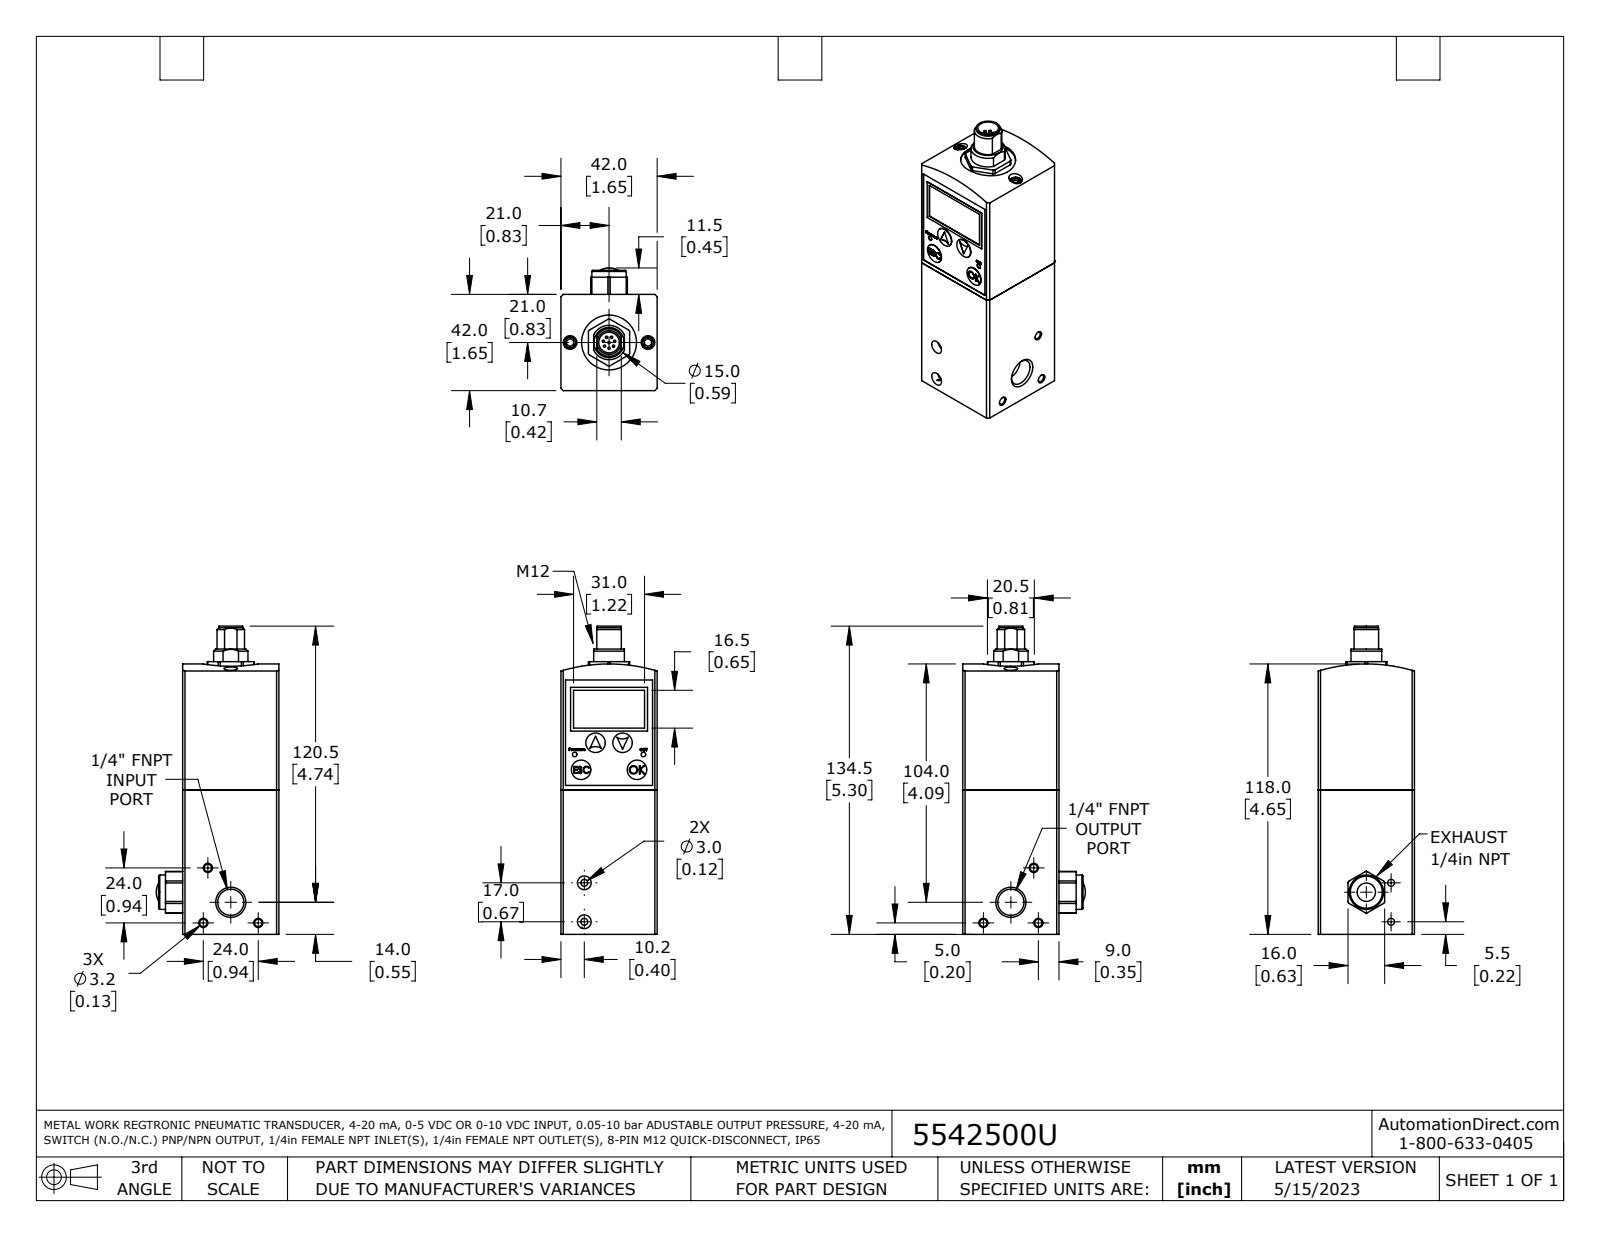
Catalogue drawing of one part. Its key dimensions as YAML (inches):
part_name: "5542500U"
step_written_by: "SolidWorks 2021 (AUTOMOTIVE_DESIGN)"
units: inches
bodies: {solids: 1, faces: 538, planar: 243, cylindrical: 248, other: 47}
overall_size: [5.295, 2.107, 1.654]
volume: 12.62
surface_area: 42.23
round_holes:
  - {diameter: 0.236, count: 8}
  - {diameter: 0.128, count: 3}
  - {diameter: 0.03, count: 2}
  - {diameter: 0.079, count: 2}
  - {diameter: 0.118, count: 2}
  - {diameter: 0.041, count: 1}
  - {diameter: 0.145, count: 1}
  - {diameter: 0.354, count: 1}
  - {diameter: 0.451, count: 1}
  - {diameter: 0.945, count: 1}
round_bosses_or_shafts:
  - {diameter: 0.039, count: 8}
  - {diameter: 0.197, count: 6}
  - {diameter: 0.335, count: 4}
  - {diameter: 0.023, count: 2}
  - {diameter: 0.591, count: 1}
  - {diameter: 0.409, count: 1}
  - {diameter: 0.117, count: 1}
  - {diameter: 0.033, count: 1}
partial_cylinders:
  - {radius: 0.039, count: 12}
  - {radius: 0.006, count: 4}
  - {radius: 0.009, count: 3}
  - {radius: 0.004, count: 2}
  - {radius: 0.004, count: 2}
  - {radius: 0.005, count: 2}
  - {radius: 0.005, count: 2}
  - {radius: 0.007, count: 2}
face_to_face_distances: [1.654, 1.646, 0.016, 1.638, 2.283, 0.276, 2.48, 1.378, 1.653, 0.015]
hole_center_spacings: [0.676, 0.882, 1.413, 0.669, 1.339, 0.591, 1.15, 1.765]
